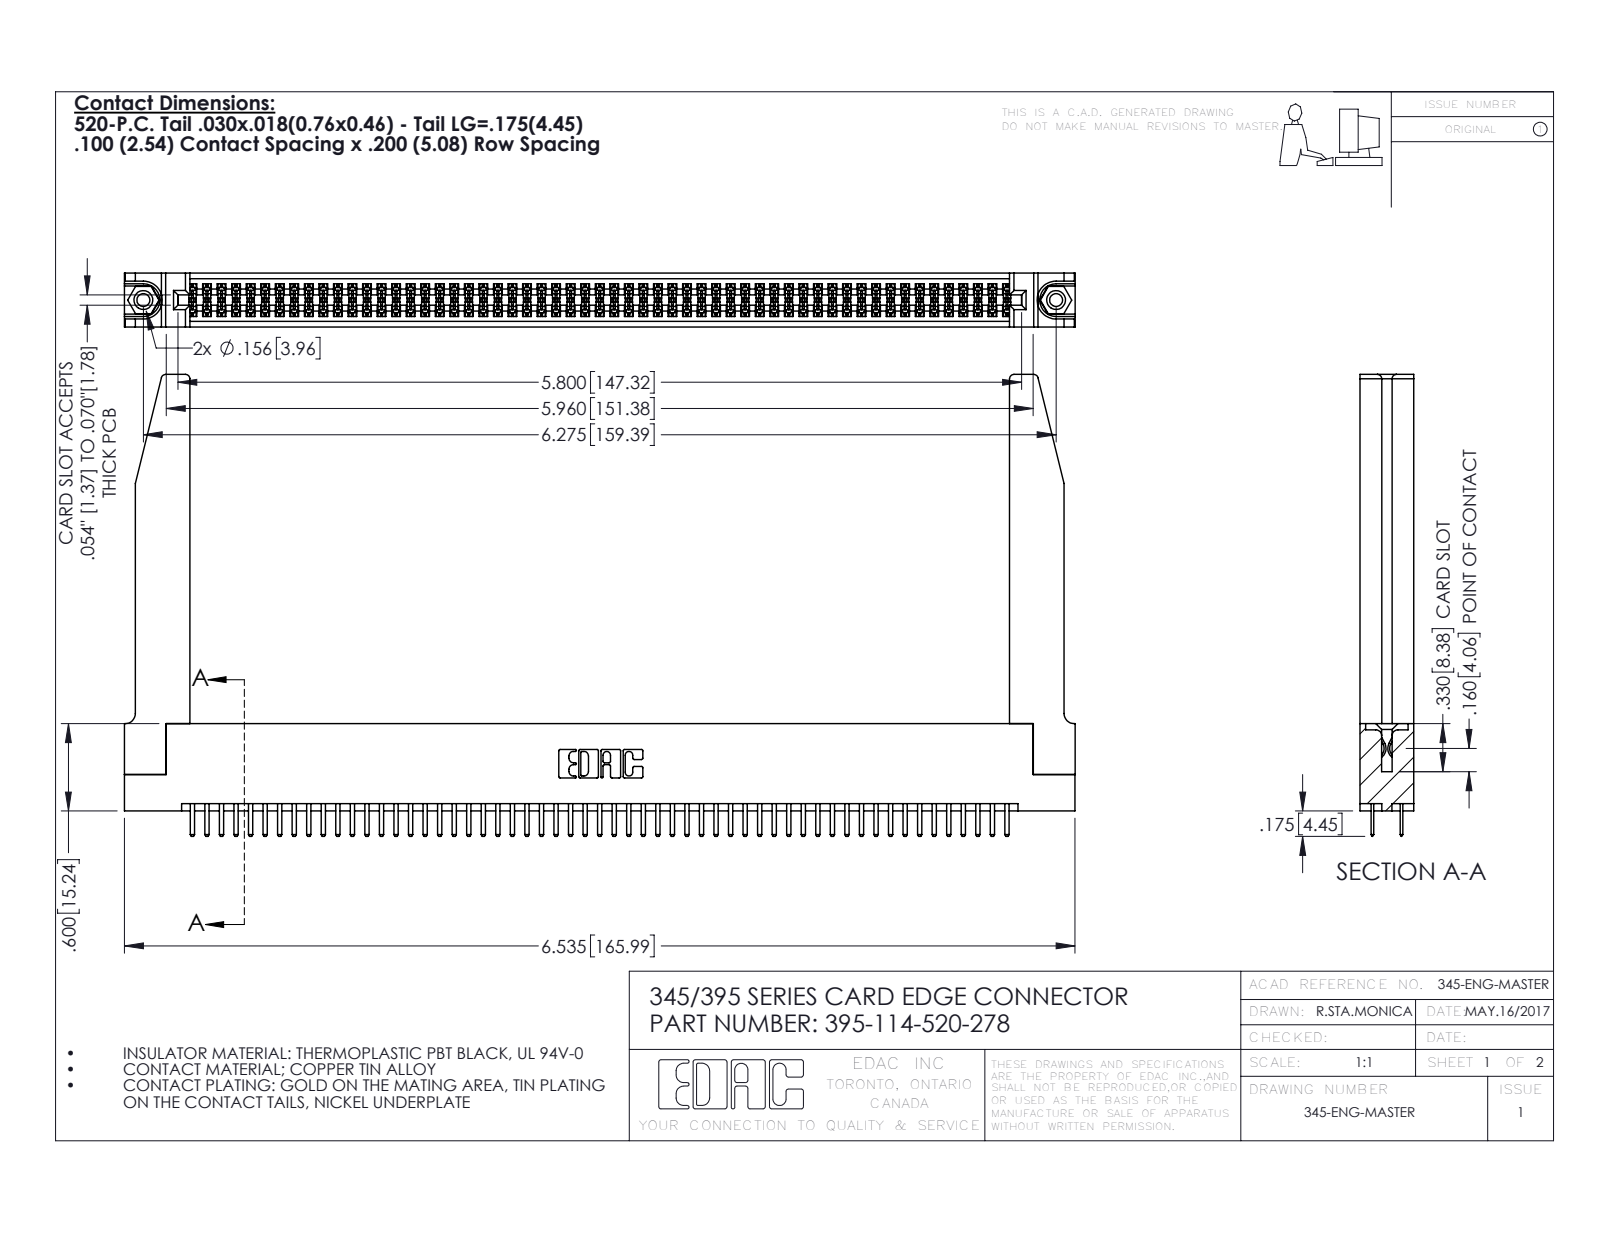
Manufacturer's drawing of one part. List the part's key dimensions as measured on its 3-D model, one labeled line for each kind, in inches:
Part name (STEP PRODUCT): 345-292-001_345-293-120; 345-250-001_345-250-001-102; 345 Part_Flush Mounting Lugs - 0.156 Dia-TH; 345-220-078_345-220-078 (+1 more)
STEP written by: SolidWorks 2016 (CONFIG_CONTROL_DESIGN)
Units: inches
Bodies: 119 solids, 6516 faces (4212 planar, 2252 cylindrical, 52 other)
Overall size (bounding box): 6.536 × 3.175 × 0.37
Volume: 1.464 in³ · Surface area: 48.04 in²
Round holes (diameter × count): ⌀0.089 ×2, ⌀0.125 ×2, ⌀0.156 ×2, ⌀0.064 ×1
Round bosses / shafts (diameter × count): ⌀0.155 ×2
Partial cylindrical surfaces — rounded edges, fillets, slot ends (radius × count): R0.006 ×171, R0.01 ×118, R0.01 ×22, R0.03 ×8, R0.007 ×6, R0.031 ×6, R0.026 ×3, R0.014 ×2
Main face-to-face distances: 0.072, 0.37, 0.298, 0.2, 0.098, 0.272, 0.025, 0.225, 0.022, 0.072
Hole centre spacings: 0.27, 6.039, 6.275
